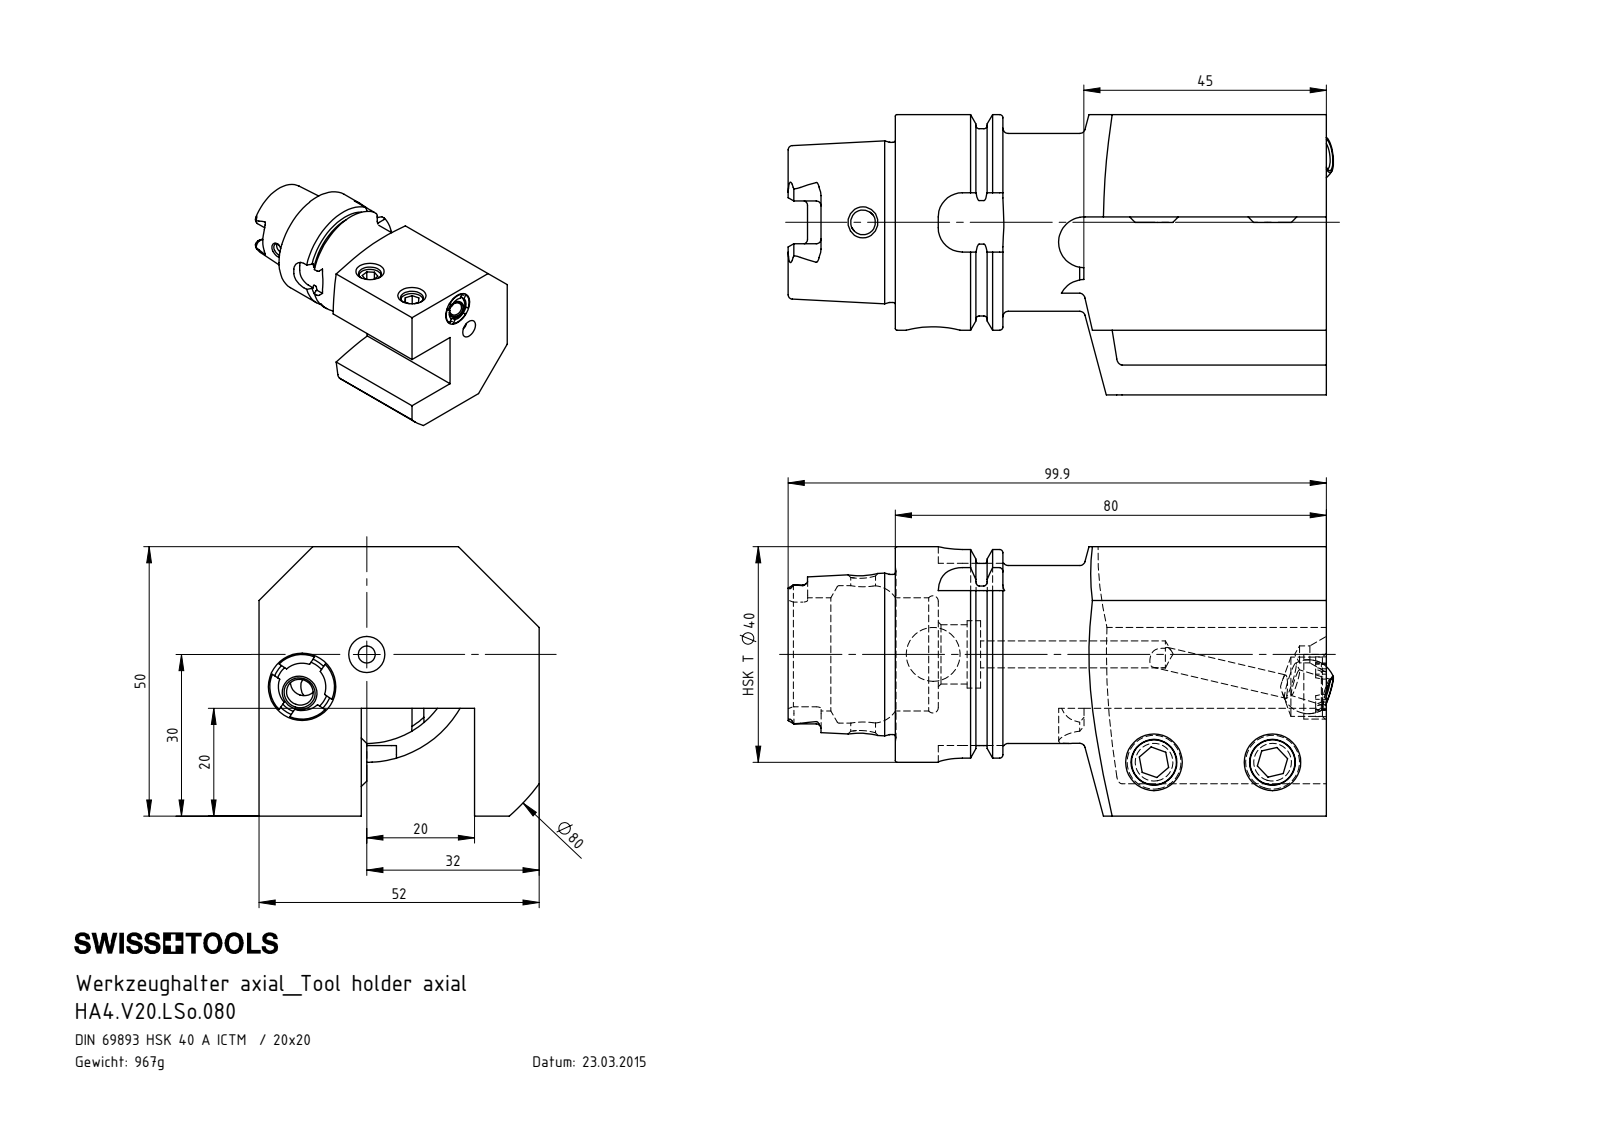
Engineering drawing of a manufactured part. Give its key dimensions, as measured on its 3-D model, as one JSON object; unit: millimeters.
{"part_name": "HA4-V20.LSo.080; KU1-U12.002.010_A; KU1-U12.003.010_A; ISO 4026 - M10 x 18 (+1 more)", "step_written_by": "SolidWorks 2012 (CONFIG_CONTROL_DESIGN)", "units": "millimeters", "bodies": {"solids": 5, "faces": 269, "planar": 93, "cylindrical": 73, "other": 103}, "overall_size": [101.21, 52, 50], "volume_mm3": 123191, "surface_area_mm2": 27212, "round_holes": [[5, 2], [8.5, 2], [10, 2], [11, 2], [3.15, 1], [4.2, 1], [4.6, 1], [12.5, 1], [21, 1], [25.5, 1]], "round_bosses_or_shafts": [[10, 2], [40, 1], [34.75, 1], [33, 1], [29.71, 1], [12, 1]], "partial_cylinders_radius": [[0.9, 6], [1.88, 4], [4.5, 4], [4.7, 2], [4.4, 1], [40, 1]], "face_to_face_distances": [52, 20, 50, 12, 30, 40, 33, 21, 19, 80], "hole_center_spacings": [13.42, 22, 45.62, 66.1]}
